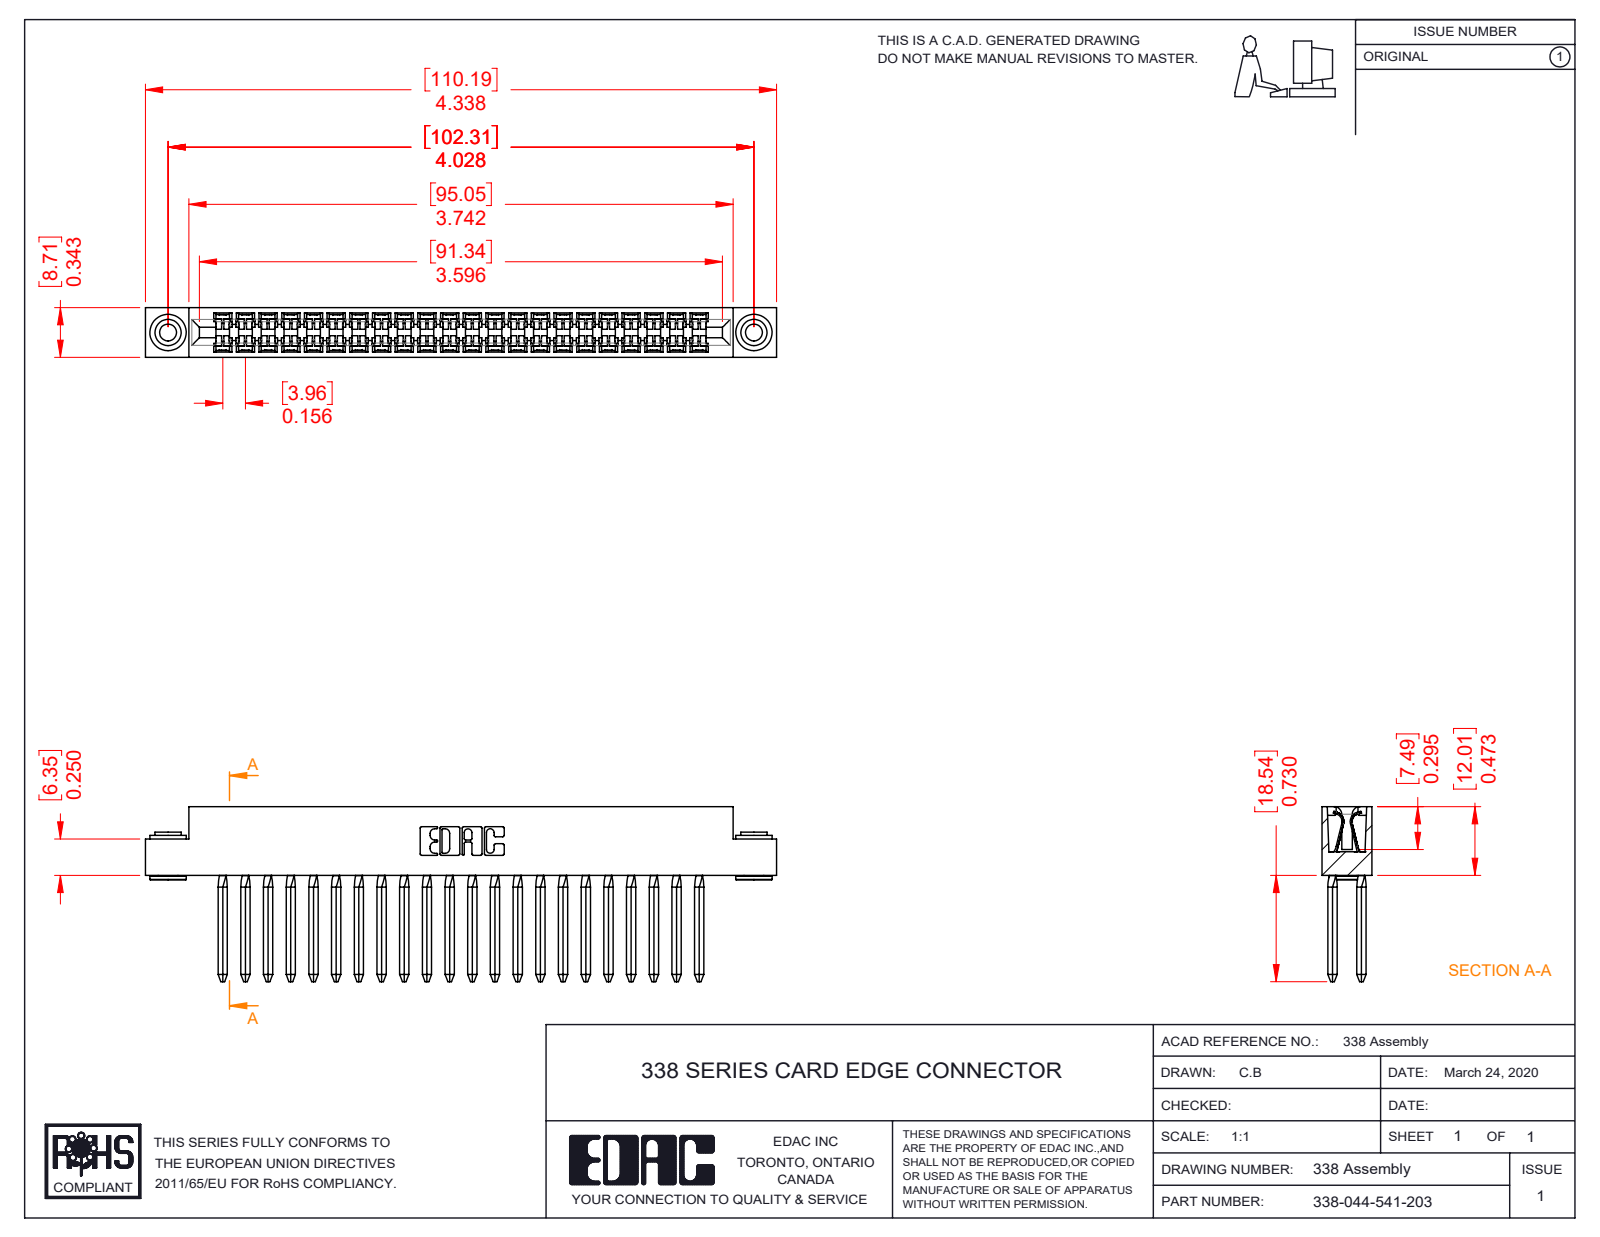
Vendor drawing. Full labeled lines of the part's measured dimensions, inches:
Part name (STEP PRODUCT): 338-290-001_541; 345-250-002_345-250-002-102; 338-044-541-203; 338-210-001_338-210-022-004
STEP written by: SolidWorks 2016 (CONFIG_CONTROL_DESIGN)
Units: inches
Bodies: 47 solids, 3094 faces (2142 planar, 768 cylindrical, 184 other)
Overall size (bounding box): 4.338 × 1.203 × 0.343
Volume: 0.517 in³ · Surface area: 24.65 in²
Round holes (diameter × count): ⌀0.116 ×2, ⌀0.156 ×2
Round bosses / shafts (diameter × count): ⌀0.25 ×2, ⌀0.18 ×2, ⌀0.136 ×2
Partial cylindrical surfaces — rounded edges, fillets, slot ends (radius × count): R0.025 ×134, R0.008 ×44, R0.055 ×36, R0.067 ×36, R0.1 ×35, R0.01 ×22, R0.007 ×6, R0.031 ×6
Main face-to-face distances: 0.343, 0.156, 0.11, 0.624, 0.207, 0.135, 0.78, 0.468, 0.221, 0.441
Hole centre spacings: 4.028
